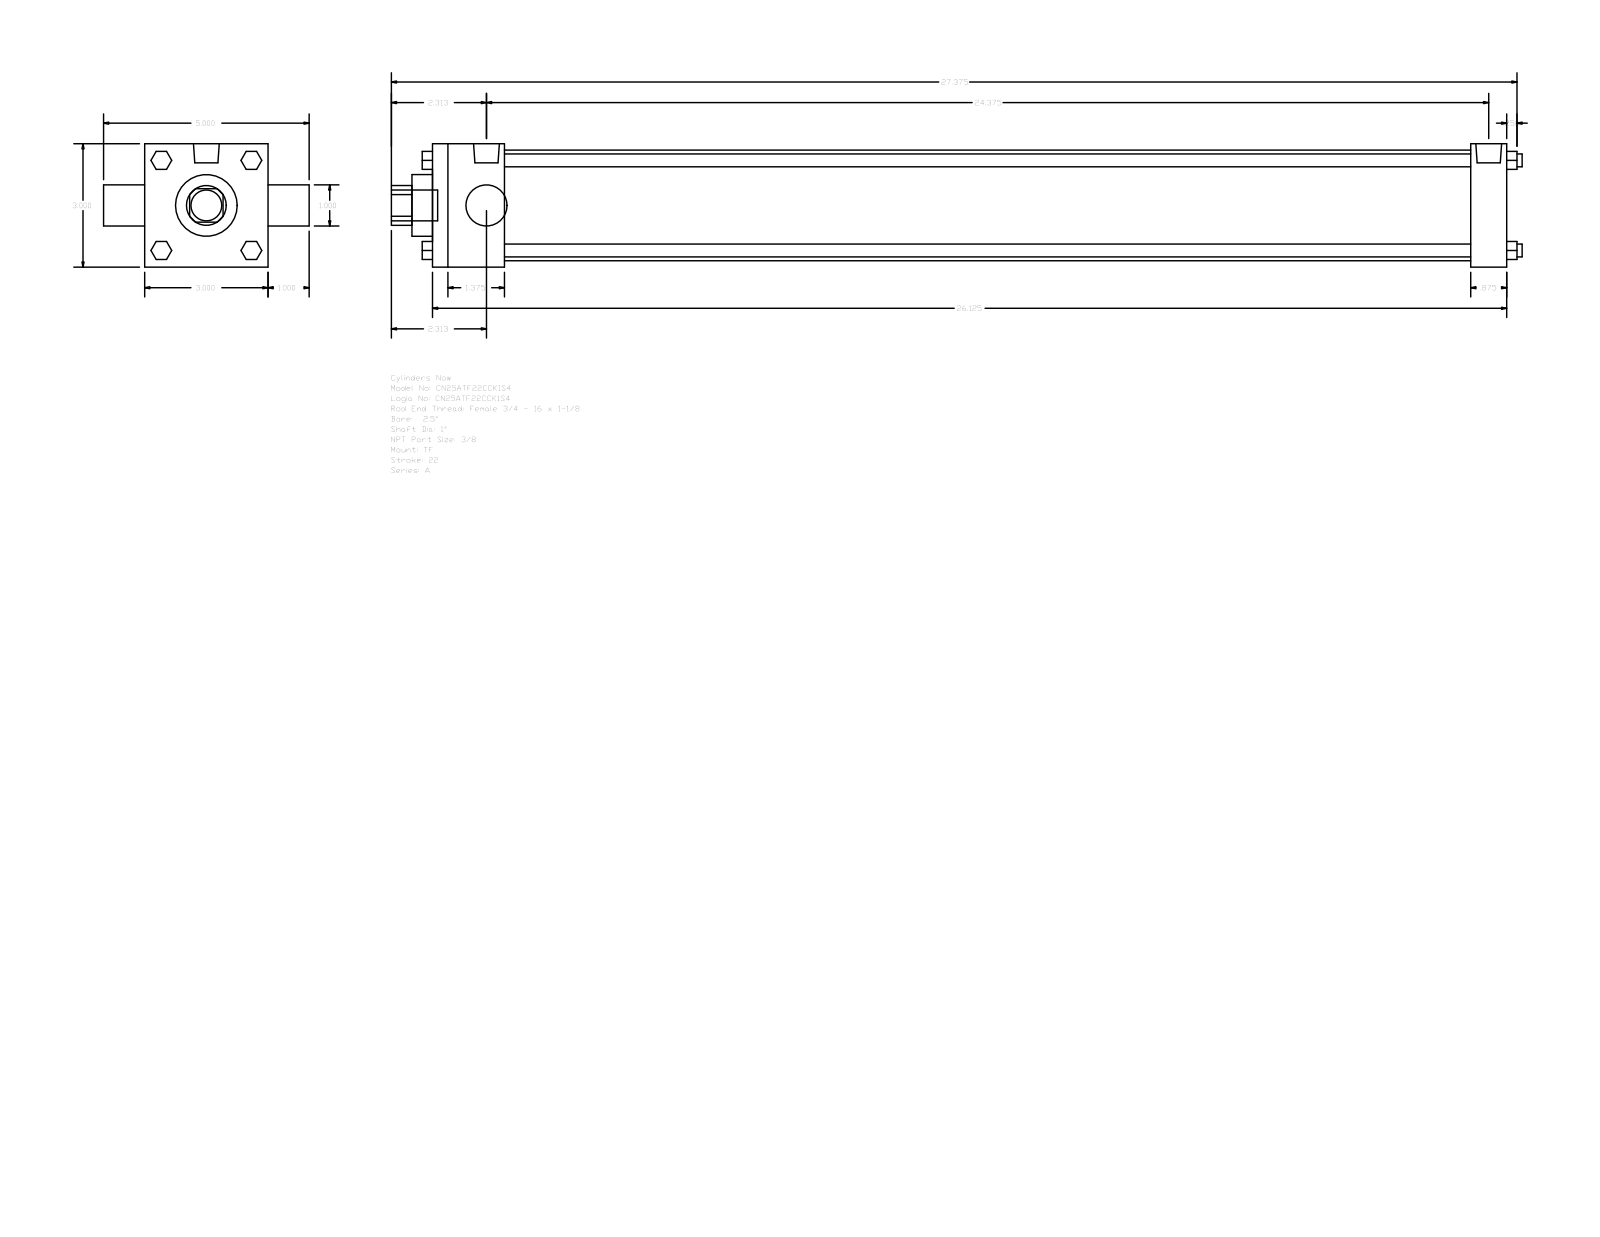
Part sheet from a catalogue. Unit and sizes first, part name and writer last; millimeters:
Units: millimetres
Overall size (bounding box): 698.5 × 127 × 76.2
Round holes (diameter × count): ⌀25.4 ×2, ⌀38.1 ×1, ⌀68.33 ×1
Round bosses / shafts (diameter × count): ⌀7.94 ×4, ⌀5.56 ×3, ⌀15.93 ×2, ⌀19.05 ×1
Partial cylindrical surfaces — rounded edges, fillets, slot ends (radius × count): R12.29 ×1
Main face-to-face distances: 76.2, 663.58, 44.45, 641.35, 596.9, 619.13, 22.23, 25.4, 101.6, 676.28
Bodies: 0 solids, 120 faces (92 planar, 28 cylindrical, 0 other)
Part name (STEP PRODUCT): A_TF__0250_1
STEP written by: GSSL Pune (CONFIG_CONTROL_DESIGN)
